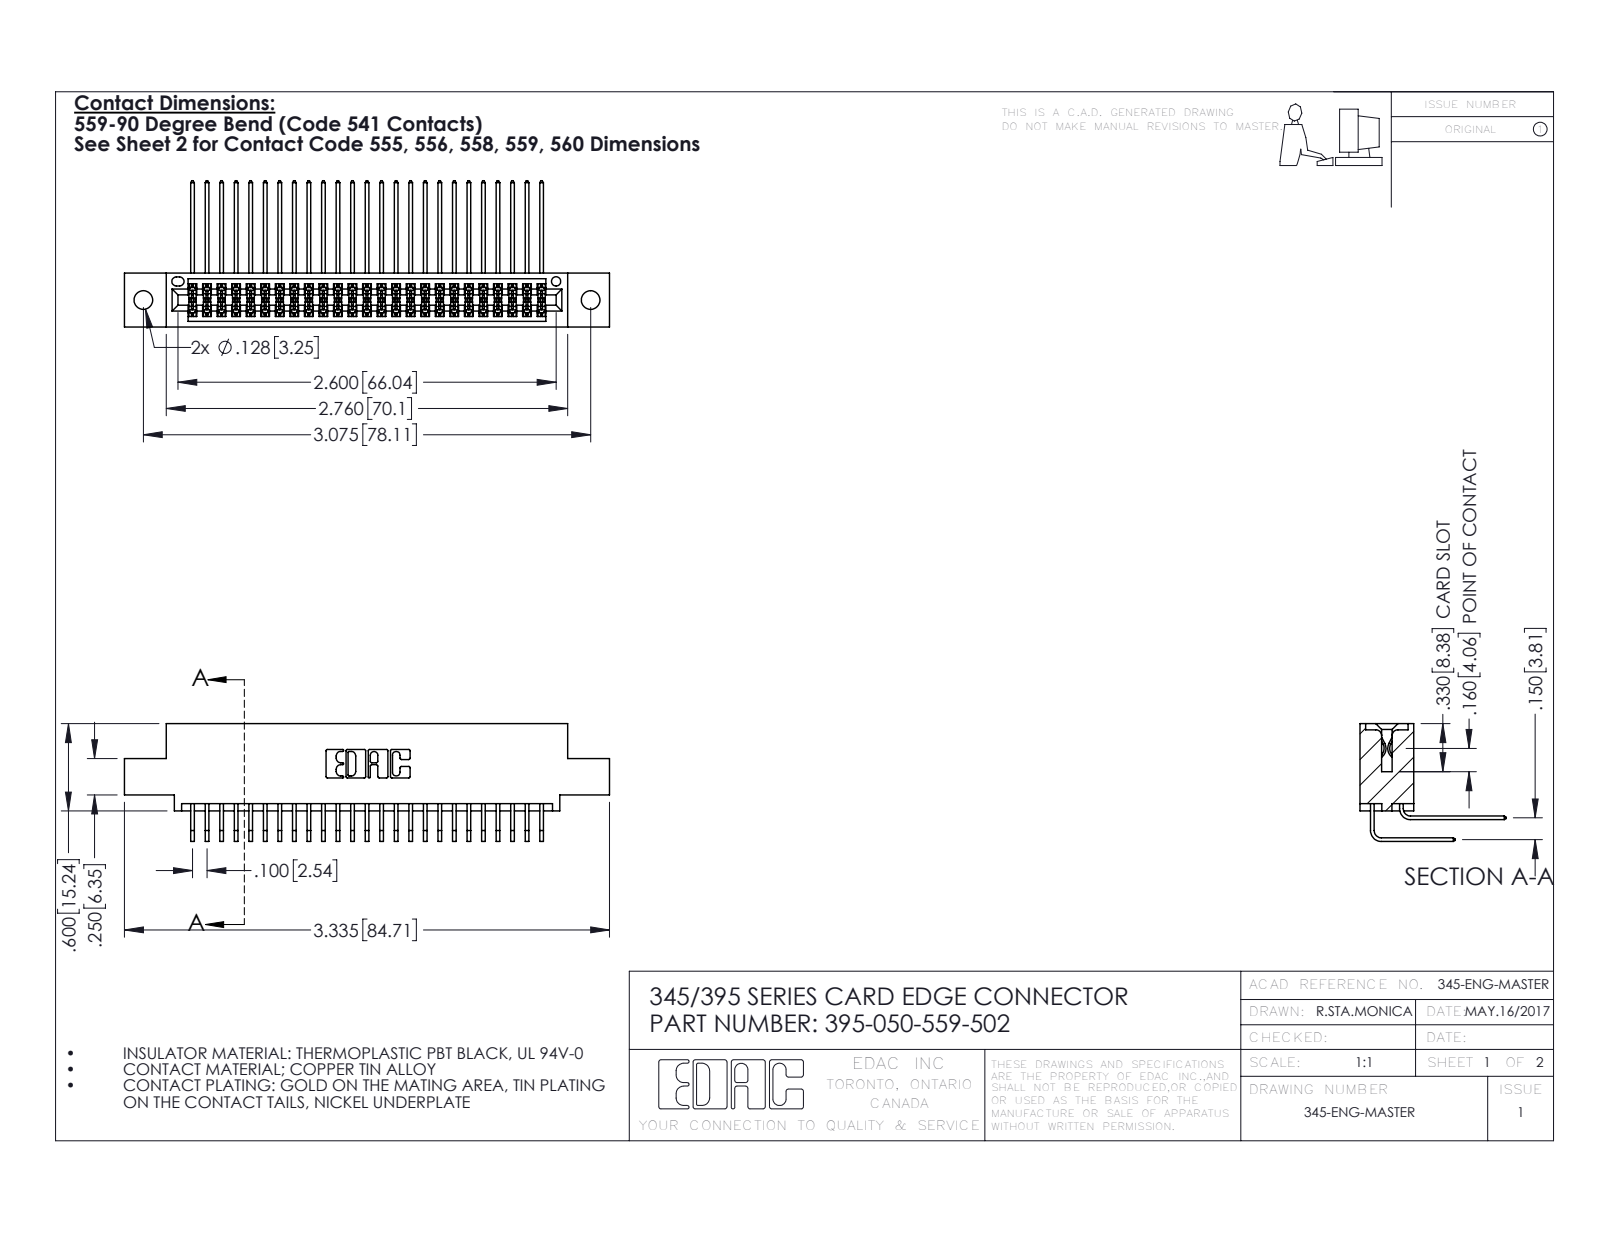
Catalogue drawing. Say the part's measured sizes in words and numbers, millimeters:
The part is named "345-292-001_558 559 Tail - 1; 345 Part_0.110 Offset - 0.128 Dia; 345-292-001_559 Tail - 2; 395-050-559-502". Its 3-D file was written by "SolidWorks 2016 (CONFIG_CONTROL_DESIGN)". It is 51 solids with 2730 faces: 1834 planar, 896 cylindrical and 0 other. Overall it measures 84.7 by 25.5 by 20.5 millimeters. Its volume is 8 240 cubic millimeters and its surface area 13 040 square millimeters. Round holes: 2 of diameter 3.3, 1 of diameter 1.6. Partial cylindrical surfaces (rounded edges, fillets, slot ends): 75 of radius 0.2, 22 of radius 0.3, 6 of radius 0.2, 6 of radius 0.8, 3 of radius 0.7, 2 of radius 0.4, 2 of radius 0.5, 2 of radius 0.6. The main face-to-face distances are 1.8, 7.6, 5.1, 9.4, 2.5, 6.9, 0.6, 5.7, 3.8, 4.4. The hole center spacings are 6.9, 72.1, 78.1.
